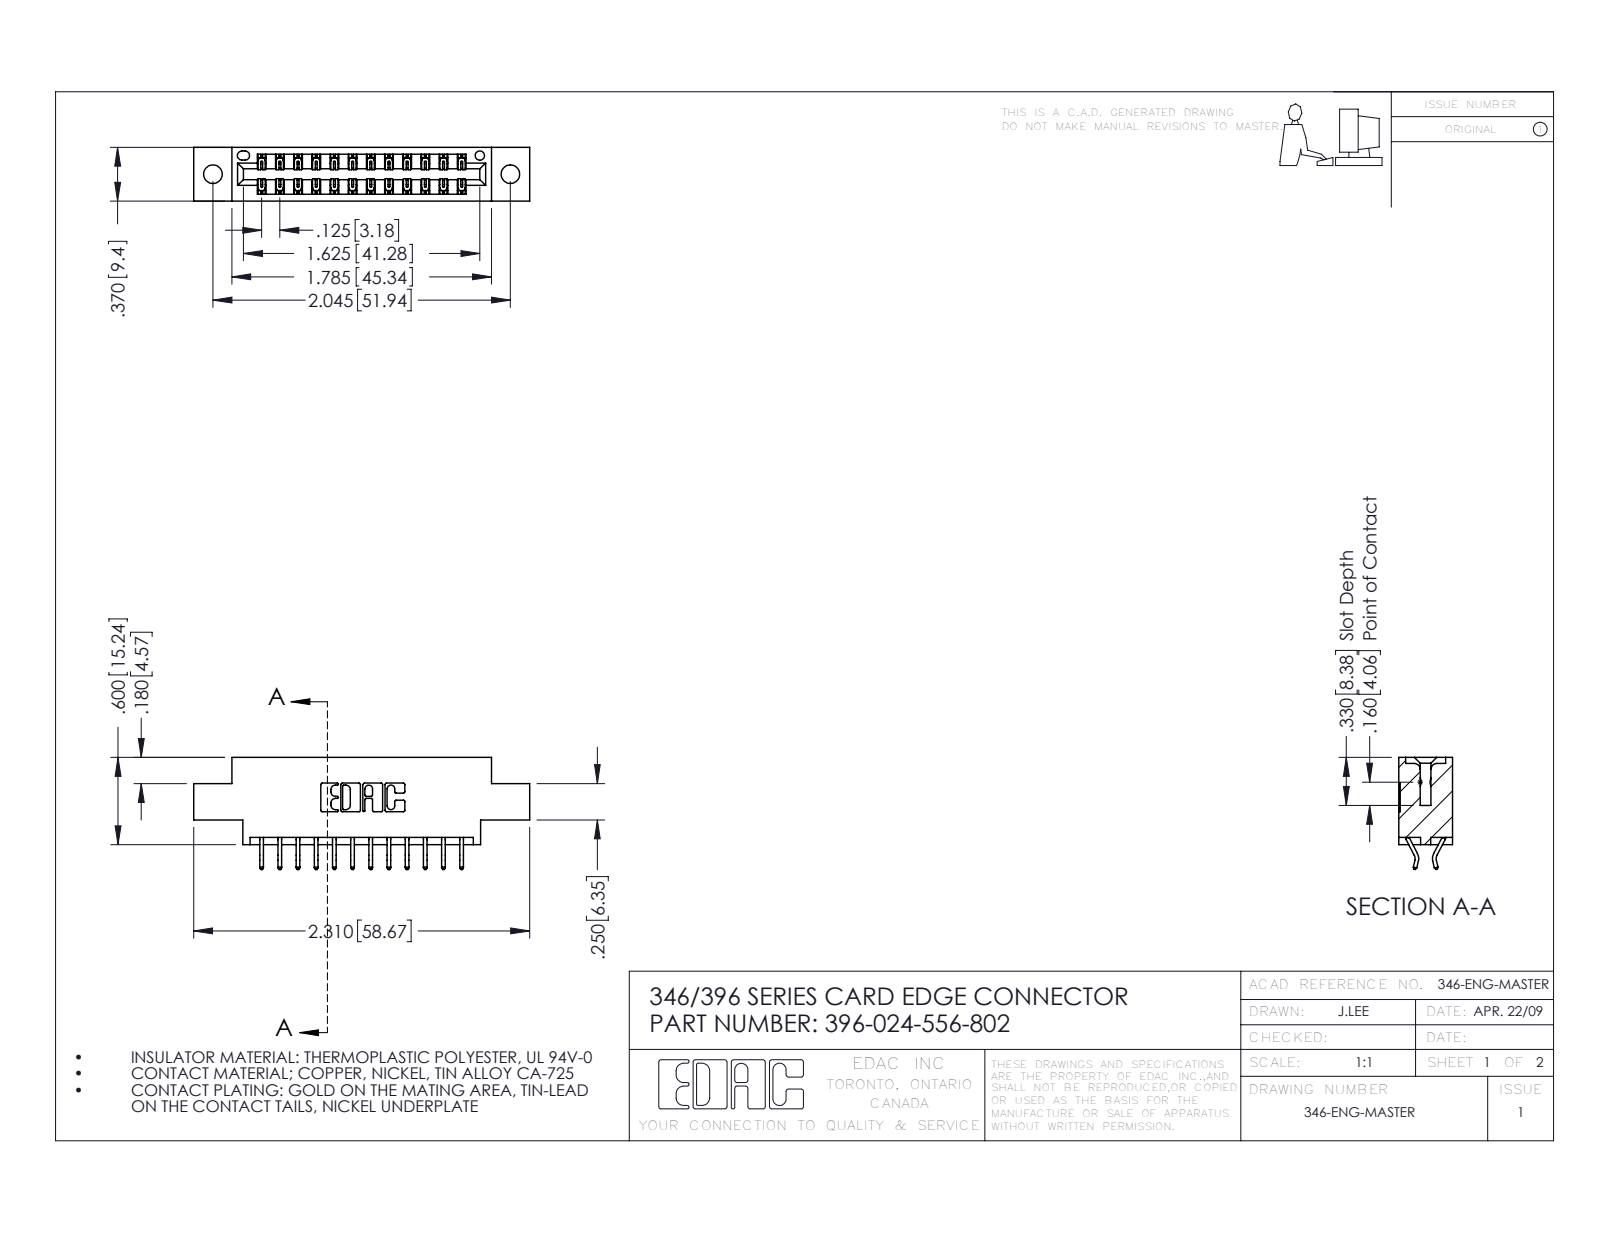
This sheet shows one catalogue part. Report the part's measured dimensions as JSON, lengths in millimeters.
{"part_name": "345-292-001_556 Tail; 346 Part_0.170 Offset - 0.128 Dia; 396-024-556-802", "step_written_by": "SolidWorks 2016 (CONFIG_CONTROL_DESIGN)", "units": "millimeters", "bodies": {"solids": 25, "faces": 1518, "planar": 1016, "cylindrical": 502, "other": 0}, "overall_size": [58.7, 19.6, 9.4], "volume_mm3": 5290, "surface_area_mm2": 6697, "round_holes": [[3.3, 2], [1.6, 1]], "partial_cylinders_radius": [[0.2, 36], [0.3, 22], [0.2, 6], [0.8, 6], [0.7, 3], [0.3, 2], [0.4, 2], [0.6, 2]], "face_to_face_distances": [6.4, 9.4, 1.2, 8.2, 0.6, 1.8, 7.6, 7, 3.8, 5.6], "hole_center_spacings": [6.2, 46.7, 51.9]}
